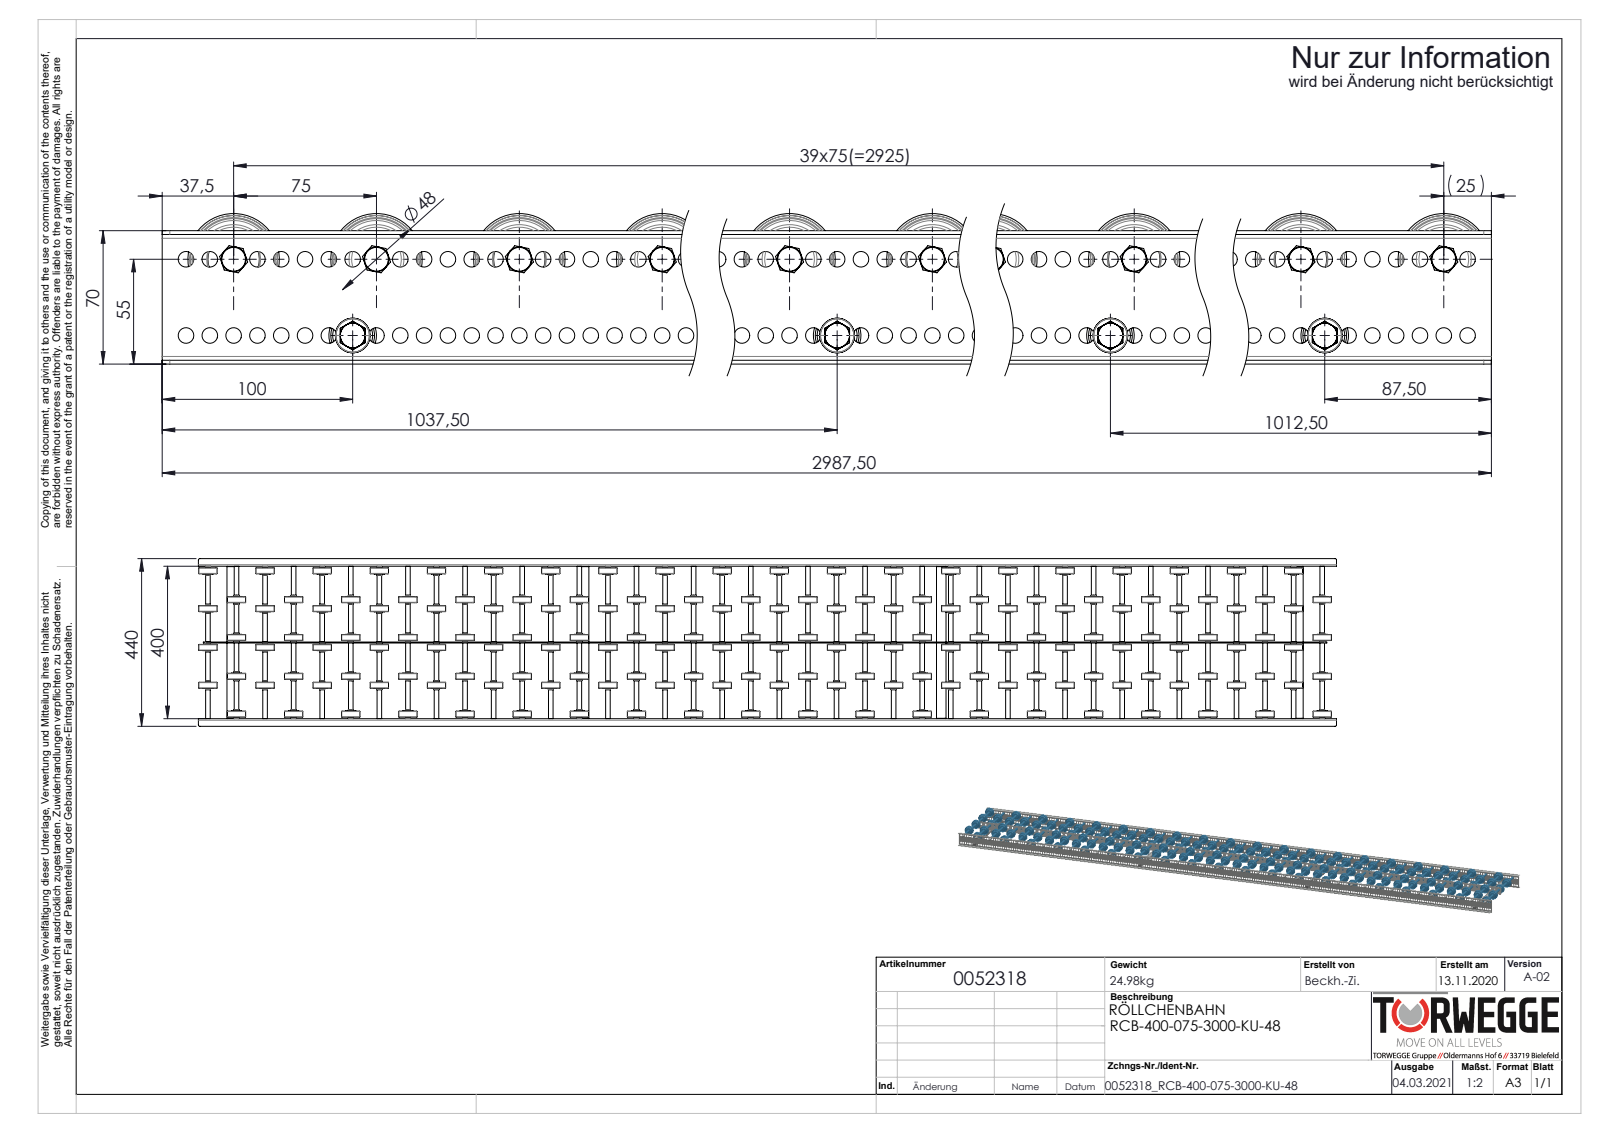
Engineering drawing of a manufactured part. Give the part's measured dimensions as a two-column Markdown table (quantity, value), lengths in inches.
| quantity | value |
| --- | --- |
| part name | S106837_Gewindestange-M8-KFG_L420; S100994_Sperrzahnschraube_M08x16-8.8-A2K; 0046278_KB-ROHR-12X1,75mm_KFG_L75,5; 0011532_2300-48-8 (+6 more) |
| STEP written by | SolidWorks 2020 (AUTOMOTIVE_DESIGN) |
| units | inches |
| bodies | 463 solids, 17218 faces (3010 planar, 6160 cylindrical, 8048 other) |
| overall size | 117.618 × 17.323 × 3.11 |
| volume | 376.6 in³ |
| surface area | 7 116 in² |
| round holes (diameter × count) | 0.323 × 476, 0.335 × 118, 0.262 × 40, 0.38 × 40, 0.539 × 40, 0.268 × 4, 0.827 × 4 |
| round bosses / shafts (diameter × count) | 0.315 × 44, 1.89 × 40, 1.063 × 40, 0.5 × 40, 0.492 × 40, 0.472 × 40, 0.984 × 4 |
| partial cylindrical surfaces (radius × count) | 0.157 × 8, 0.079 × 4, 0.197 × 4 |
| main face-to-face distances | 0.079, 15.827, 2.677, 15.906, 15.748, 7.917, 7.819, 7.909, 7.831, 7.996 |
| hole center spacings | 0.492, 0.984, 1.476, 1.969, 2.461, 2.953, 3.445, 3.937 |
